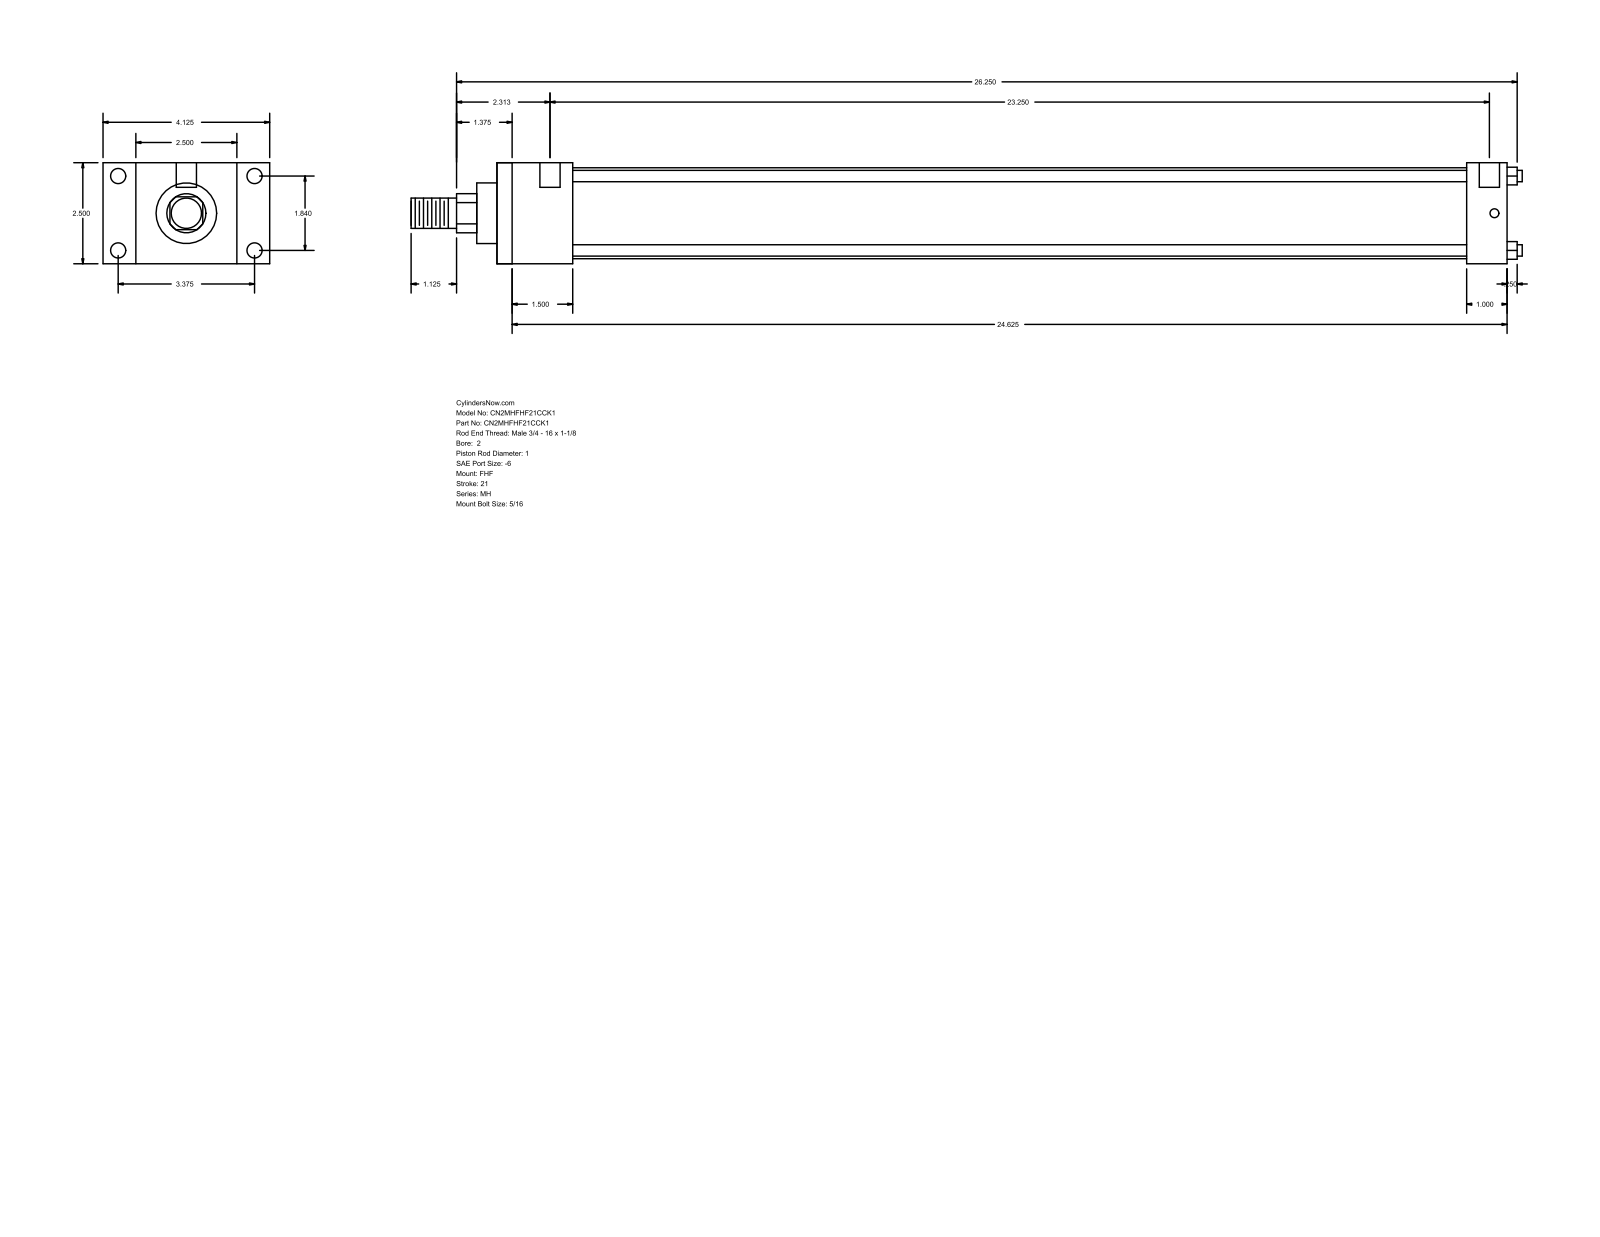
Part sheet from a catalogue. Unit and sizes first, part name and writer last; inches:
Units: inches
Overall size (bounding box): 27.5 × 4.125 × 2.5
Round holes (diameter × count): ⌀0.219 ×4, ⌀0.375 ×4, ⌀0.5 ×2
Round bosses / shafts (diameter × count): ⌀0.281 ×4, ⌀2.25 ×1, ⌀1.5 ×1, ⌀1 ×1, ⌀0.75 ×1
Partial cylindrical surfaces — rounded edges, fillets, slot ends (radius × count): R0.484 ×1
Main face-to-face distances: 2.5, 25, 1.875, 23.125, 0.813, 3.313, 4.125, 1, 24, 22.125
Hole centre spacings: 1.84, 3.375, 3.844, 23.562, 0.125, 0.187, 23.25, 23.375
Bodies: 0 solids, 88 faces (60 planar, 28 cylindrical, 0 other)
Part name (STEP PRODUCT): MH_FHF__0200_1
STEP written by: GSSL Pune (CONFIG_CONTROL_DESIGN)
